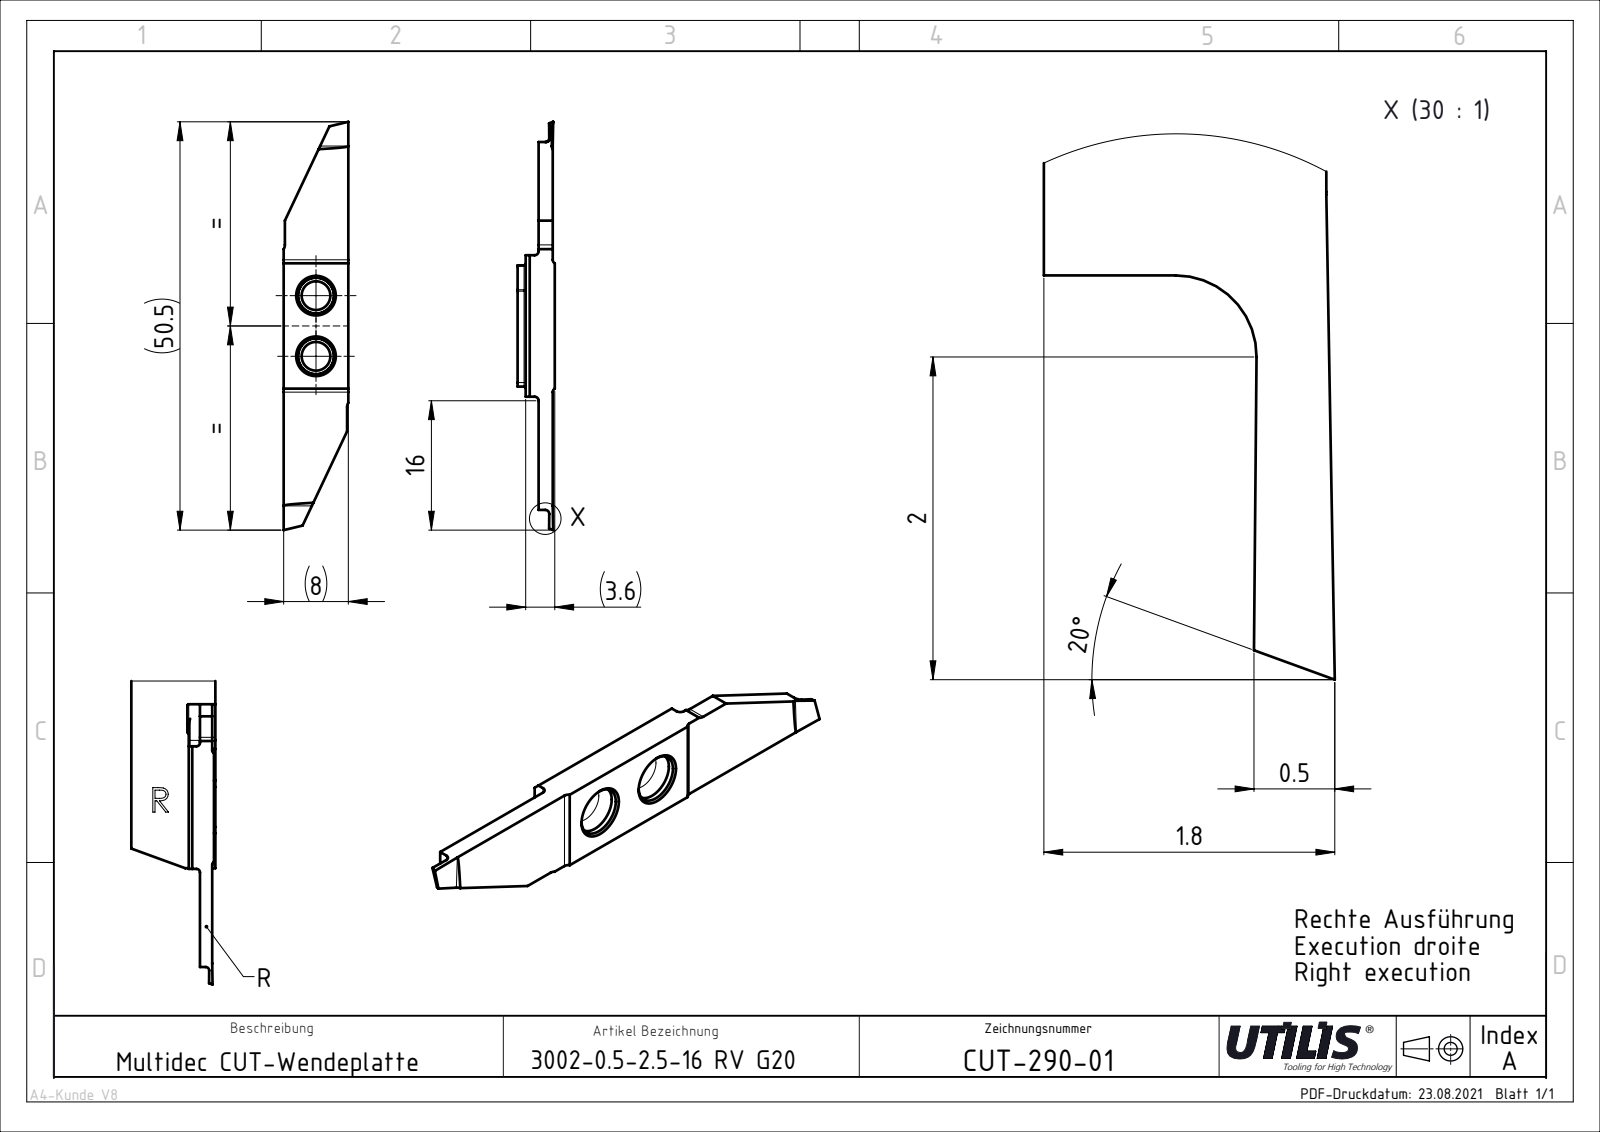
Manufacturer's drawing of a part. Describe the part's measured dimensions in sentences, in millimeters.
The part is named "CUT-290-01". Its 3-D file was written by "SolidWorks 2016 (AUTOMOTIVE_DESIGN)". It is 1 solid with 38 faces: 24 planar, 14 cylindrical and 0 other. Overall it measures 50.5 by 8 by 3.55 millimeters. Its volume is 736 cubic millimeters and its surface area 953 square millimeters. Round holes: 2 of diameter 3.55. Partial cylindrical surfaces (rounded edges, fillets, slot ends): 6 of radius 0.5, 2 of radius 0.15, 2 of radius 1. The main face-to-face distances are 1.75, 1.55, 3.3, 3.55, 2, 8, 18.1, 7.85, 17.5, 7.7. The hole center spacings are 7.5.
